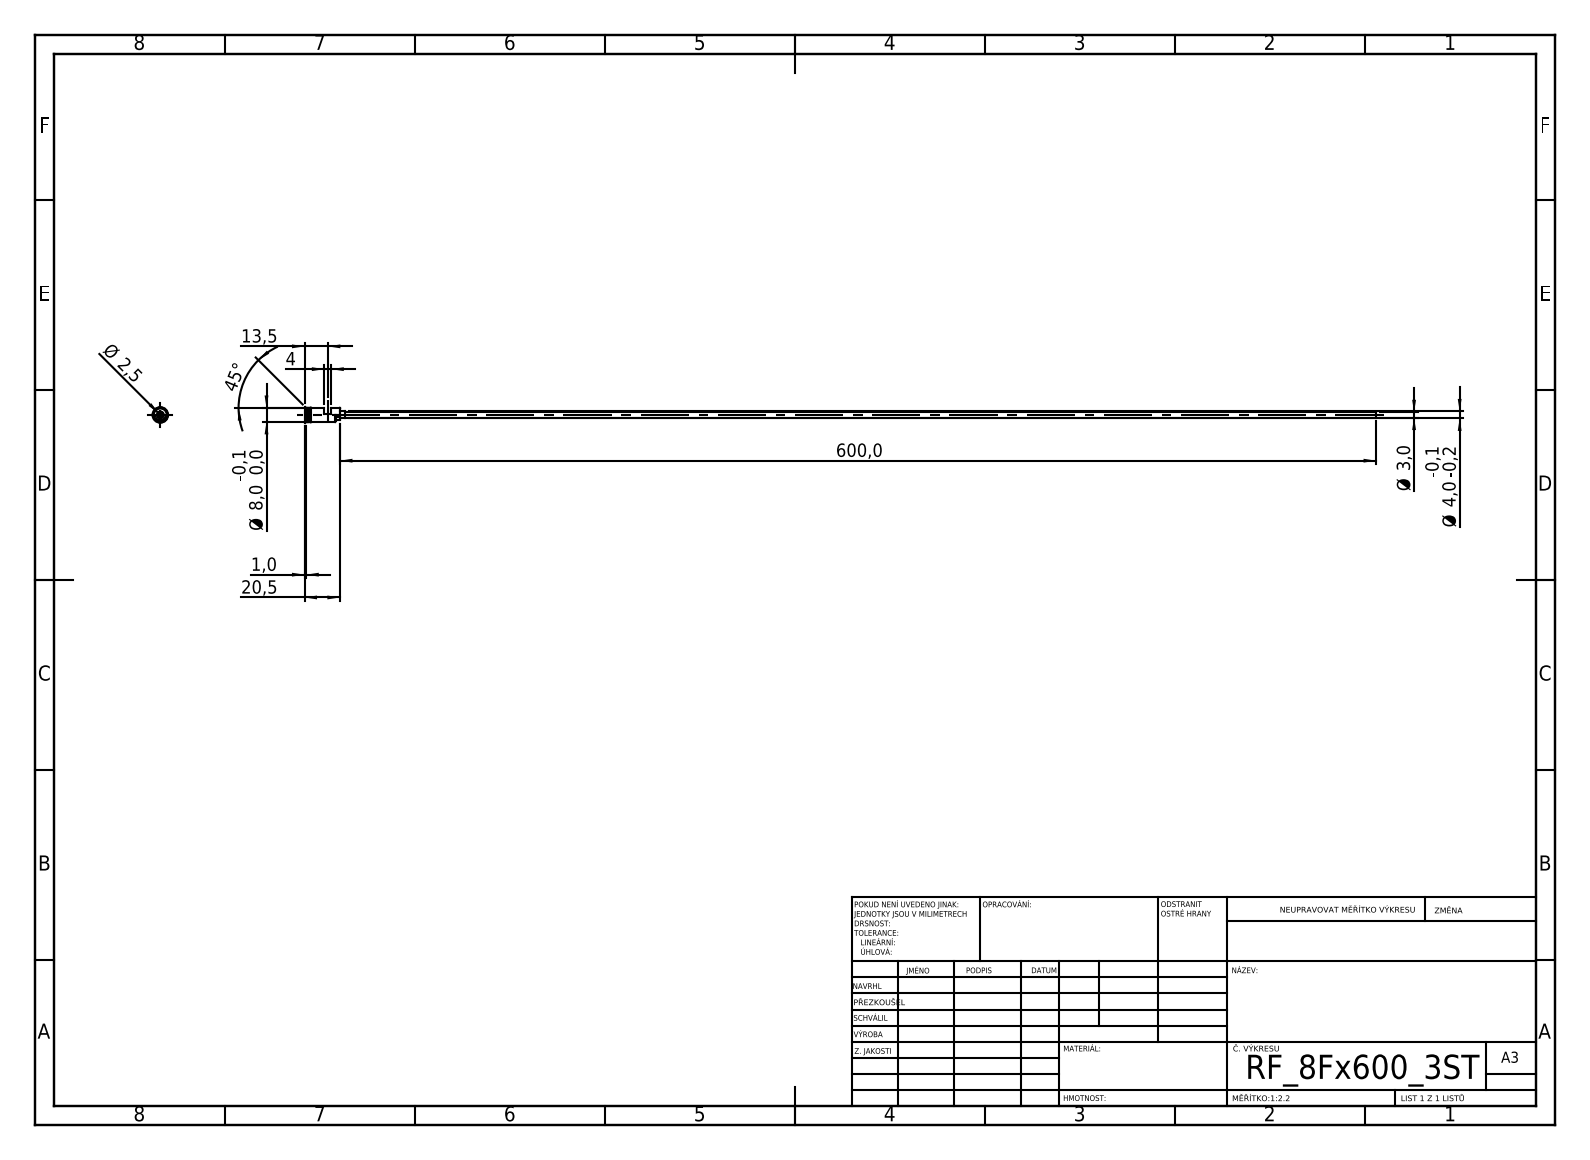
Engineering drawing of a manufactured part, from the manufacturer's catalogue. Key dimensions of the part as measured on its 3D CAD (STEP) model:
STEP written by: SolidWorks 2019 (CONFIG_CONTROL_DESIGN)
Units: millimetres
Bodies: 1 solid, 55 faces (24 planar, 19 cylindrical, 12 other)
Overall size (bounding box): 620.5 × 9 × 9
Volume: 2 181 mm³ · Surface area: 11 122 mm²
Round holes (diameter × count): ⌀2.5 ×1
Round bosses / shafts (diameter × count): ⌀9 ×1, ⌀8 ×1, ⌀7.8 ×1, ⌀4 ×1, ⌀3 ×1
Partial cylindrical surfaces — rounded edges, fillets, slot ends (radius × count): R3 ×2, R3.05 ×1
Main face-to-face distances: 4, 20.5, 9, 11.5, 5, 15.5, 2.5, 18.5, 13.5, 9.5
